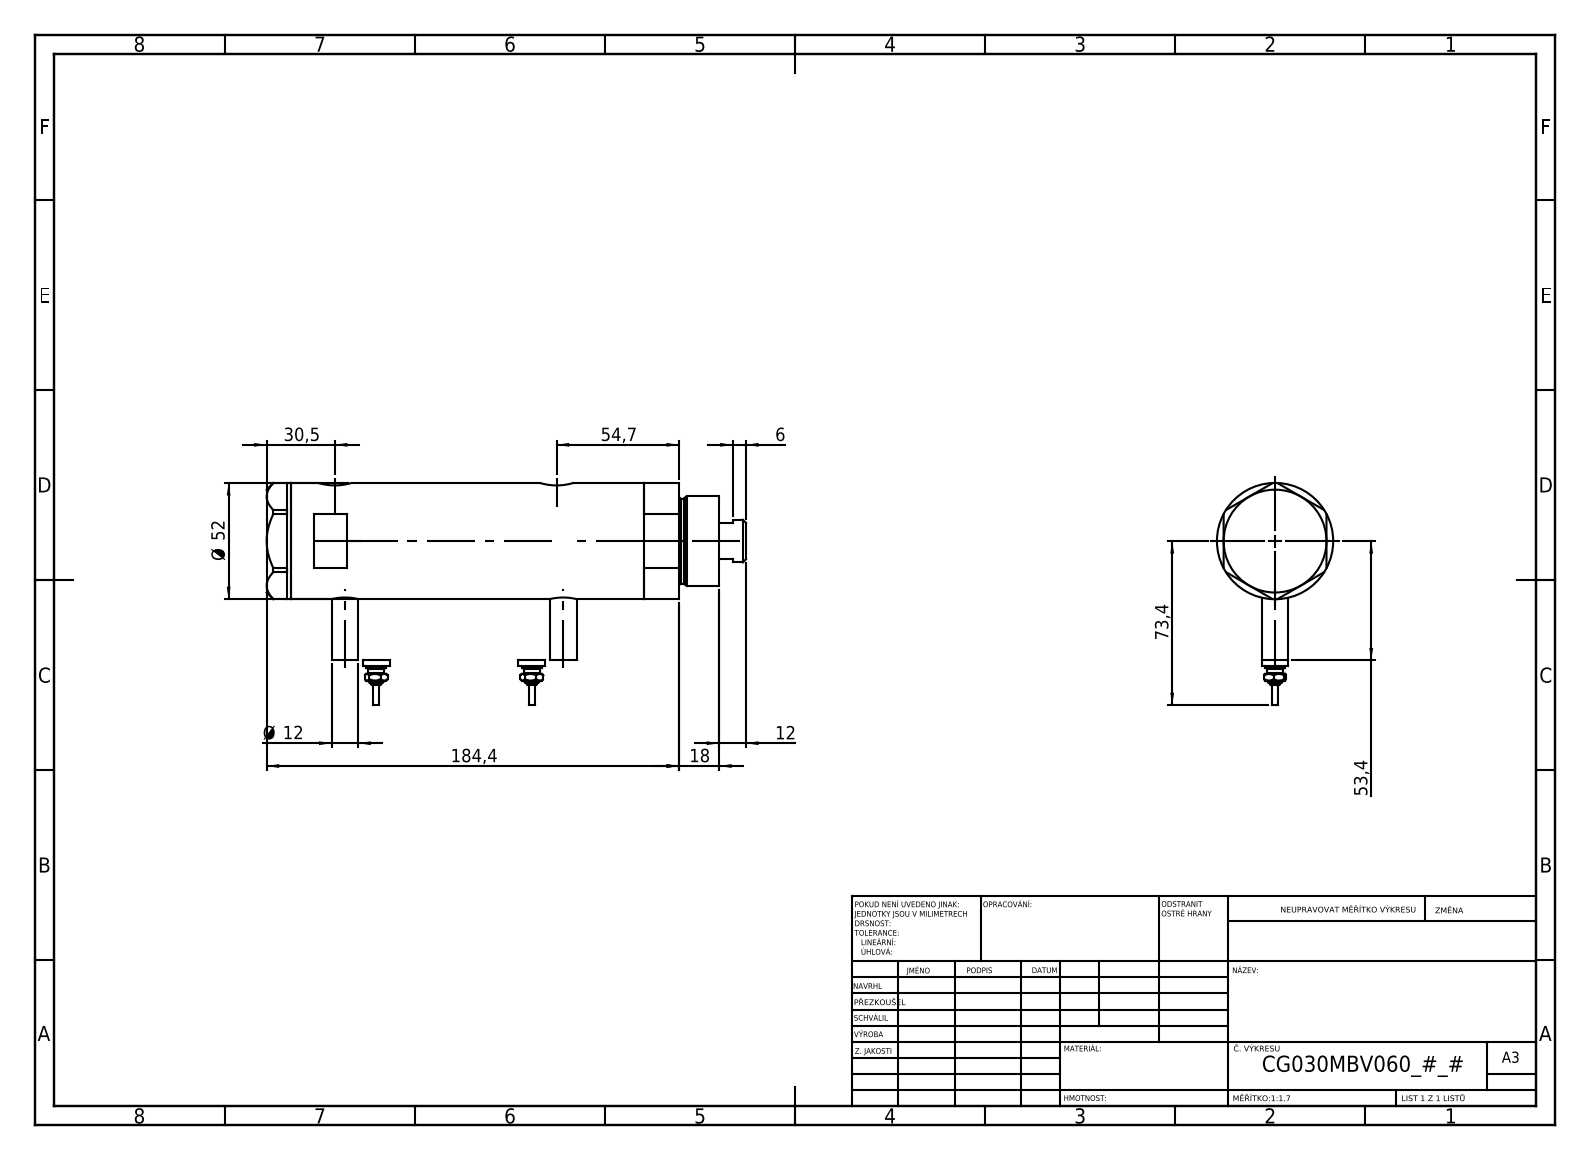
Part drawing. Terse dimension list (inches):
name: Switch; V270CG_BACK; V270CG_VC; V270CG_MIDDLE (+1 more)
written by: SolidWorks 2019 (CONFIG_CONTROL_DESIGN)
unit: in
bodies: 6 solids, 226 faces (93 planar, 69 cylindrical, 64 other)
size: 8.441 × 3.913 × 2.047
volume: 23.97 in³; area: 138.8 in²
holes: 2× ⌀0.383, 2× ⌀0.492, 2× ⌀0.591, 1× ⌀0.256, 1× ⌀0.787, 1× ⌀0.846, 1× ⌀1.181, 1× ⌀1.299, 1× ⌀1.732
bosses: 4× ⌀0.472, 2× ⌀0.354, 2× ⌀0.276, 2× ⌀0.177, 2× ⌀0.098, 1× ⌀2.047, 1× ⌀1.575, 1× ⌀1.496
face distances: 4.783, 0.937, 3.846, 0.433, 1.37, 5.217, 1.811, 1.433, 6.65, 6.217
hole spacings: 0.114, 0.177, 3.728, 3.843, 3.906, 4.02
